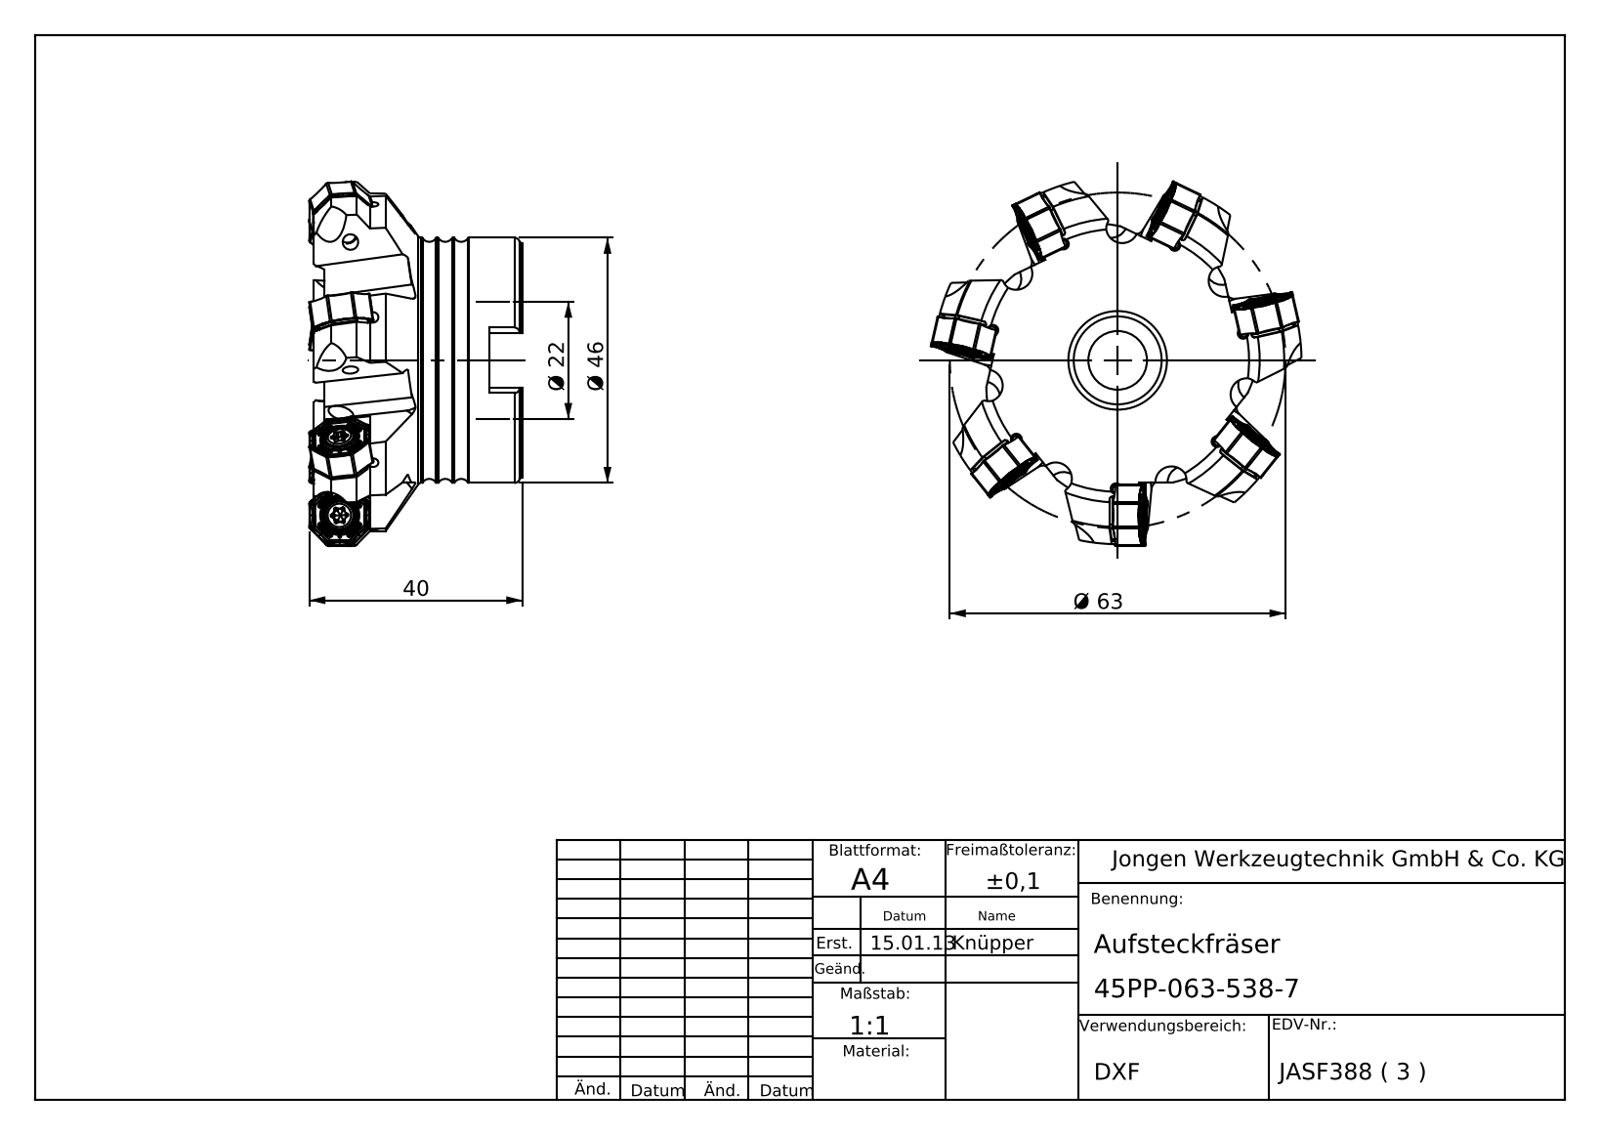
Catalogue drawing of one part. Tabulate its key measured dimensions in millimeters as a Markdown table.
| quantity | value |
| --- | --- |
| part name | 45PP-063-538-7 |
| STEP written by | SolidWorks 2013 (AUTOMOTIVE_DESIGN) |
| units | millimeters |
| bodies | 1 solid, 282 faces (90 planar, 92 cylindrical, 100 other) |
| overall size | 70.94 × 70.94 × 40.05 |
| volume | 77 194 mm³ |
| surface area | 18 039 mm² |
| round holes (diameter × count) | 3 × 7, 11 × 1, 16.5 × 1, 22 × 1, 22.15 × 1, 22.3 × 1 |
| round bosses / shafts (diameter × count) | 46 × 1 |
| partial cylindrical surfaces (radius × count) | 1 × 14, 1.25 × 7, 3 × 7, 32.05 × 1 |
| main face-to-face distances | 37.1, 6.25, 30.85, 19.95, 13.7, 17.15, 10.4, 26.1, 19.85, 6.15 |
